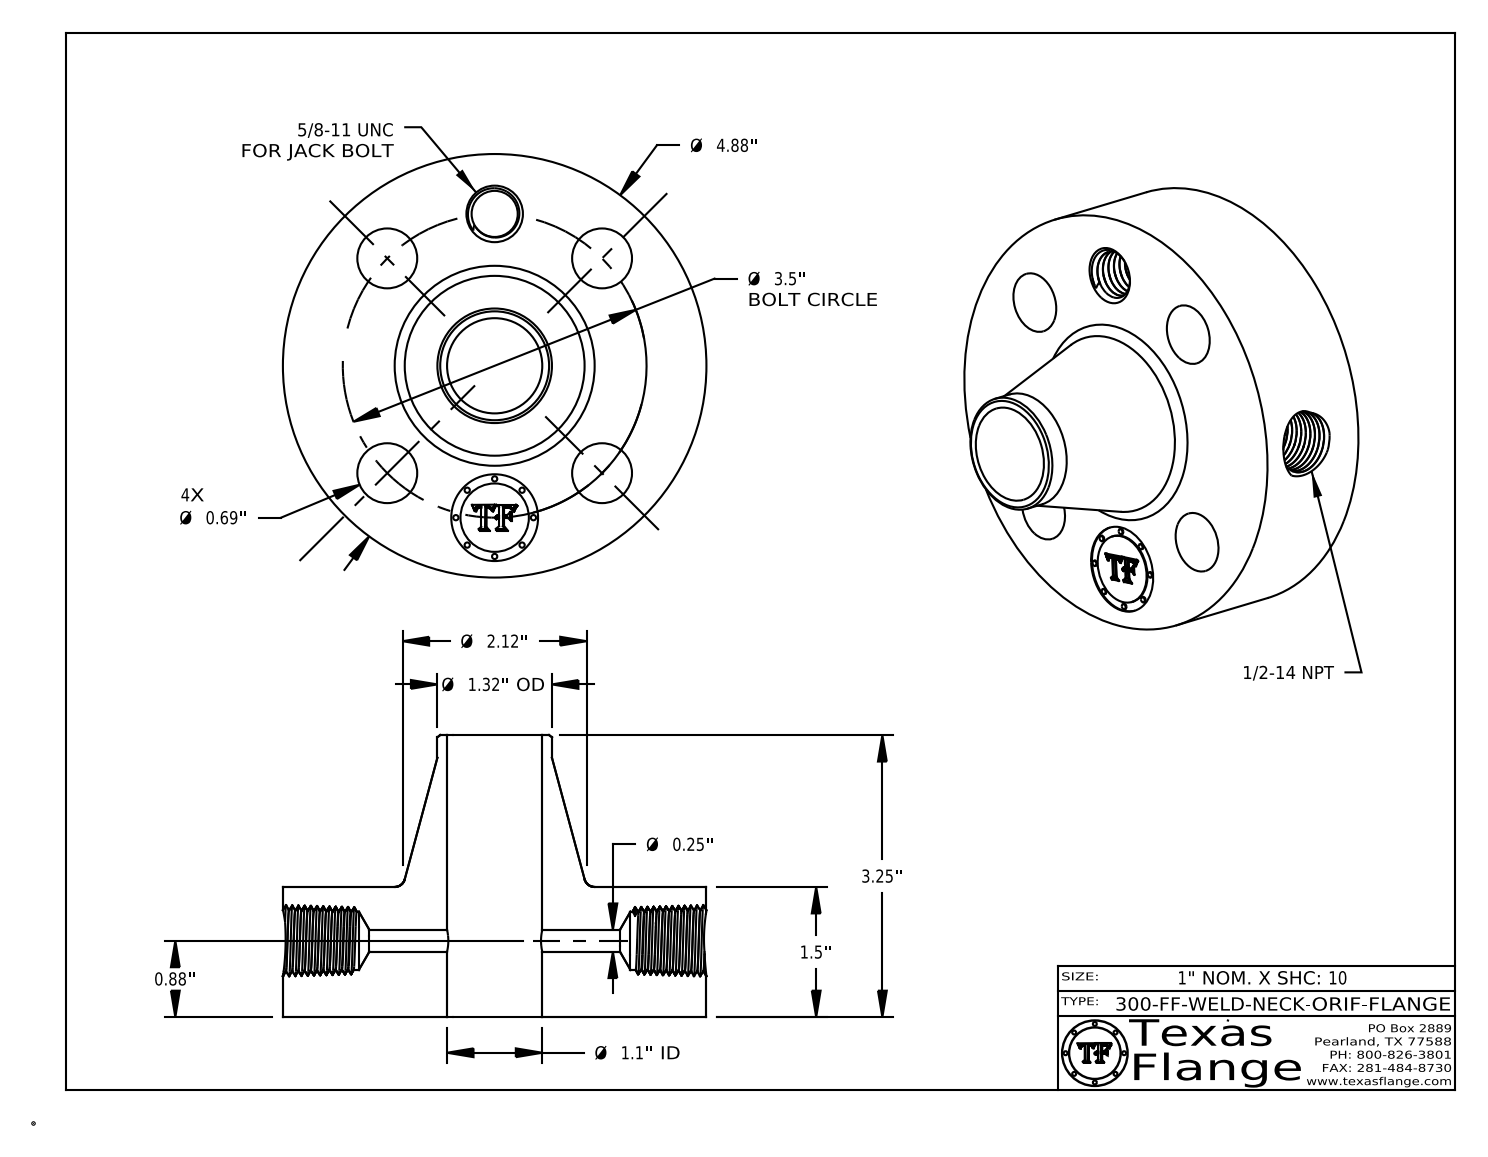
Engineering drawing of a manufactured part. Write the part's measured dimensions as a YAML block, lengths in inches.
part_name: "300-FF-WELD-NECK"
step_written_by: "CATIA V5 STEP AP214 (AUTOMOTIVE_DESIGN)"
units: inches
bodies: {solids: 1, faces: 761, planar: 368, cylindrical: 85, other: 308}
overall_size: [4.88, 4.88, 3.25]
volume: 25.36
surface_area: 98.47
round_holes:
  - {diameter: 0.69, count: 4}
  - {diameter: 0.25, count: 1}
  - {diameter: 0.531, count: 1}
  - {diameter: 0.672, count: 1}
  - {diameter: 1, count: 1}
  - {diameter: 1.097, count: 1}
round_bosses_or_shafts:
  - {diameter: 0.061, count: 8}
  - {diameter: 4.88, count: 1}
  - {diameter: 1.32, count: 1}
  - {diameter: 0.788, count: 1}
face_to_face_distances: [1.5, 1.485, 0.015, 3.25, 1.765, 1.75, 0.298, 0.293, 0.054, 0.248]
hole_center_spacings: [1.75, 1.339, 2.475, 3.233, 3.5]
